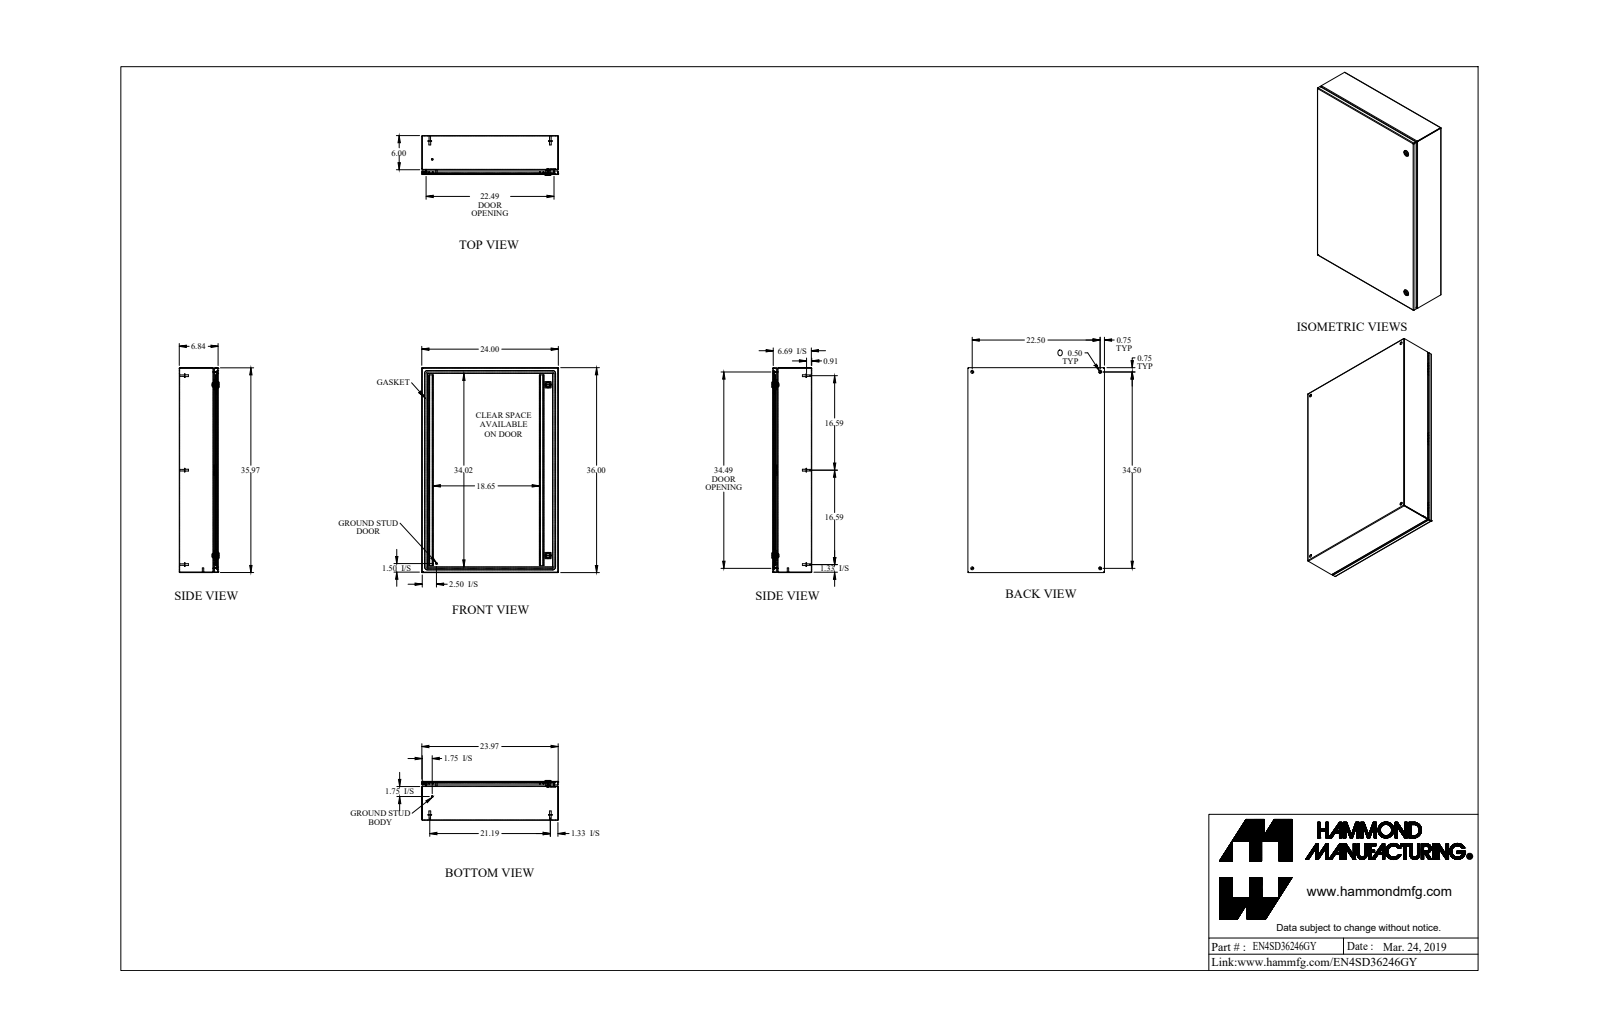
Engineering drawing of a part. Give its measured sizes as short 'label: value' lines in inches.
name: EN4SD36246GY_Default
written by: SolidWorks 2019 (CONFIG_CONTROL_DESIGN)
unit: in
bodies: 33 solids, 917 faces (430 planar, 307 cylindrical, 180 other)
size: 36 × 24 × 6.997
volume: 209.7 in³; area: 5 894 in²
holes: 4× ⌀0.5, 2× ⌀0.232, 2× ⌀0.625, 2× ⌀0.785, 1× ⌀0.172, 1× ⌀0.24, 1× ⌀0.242
bosses: 6× ⌀0.625, 6× ⌀0.313, 6× ⌀0.27, 2× ⌀1.1, 2× ⌀0.525, 2× ⌀0.281, 2× ⌀0.25, 1× ⌀0.455
rounds: 20× R0.036, 20× R0.108, 12× R0.043, 12× R0.081, 12× R0.382, 8× R19.003, 6× R0.006, 6× R0.062
face distances: 0.072, 6.765, 6.693, 6.837, 23.928, 35.928, 23.856, 24, 0.837, 5.928
hole spacings: 22.5, 34.5, 41.189, 2.493, 2.494, 21.545, 21.545, 29.999
